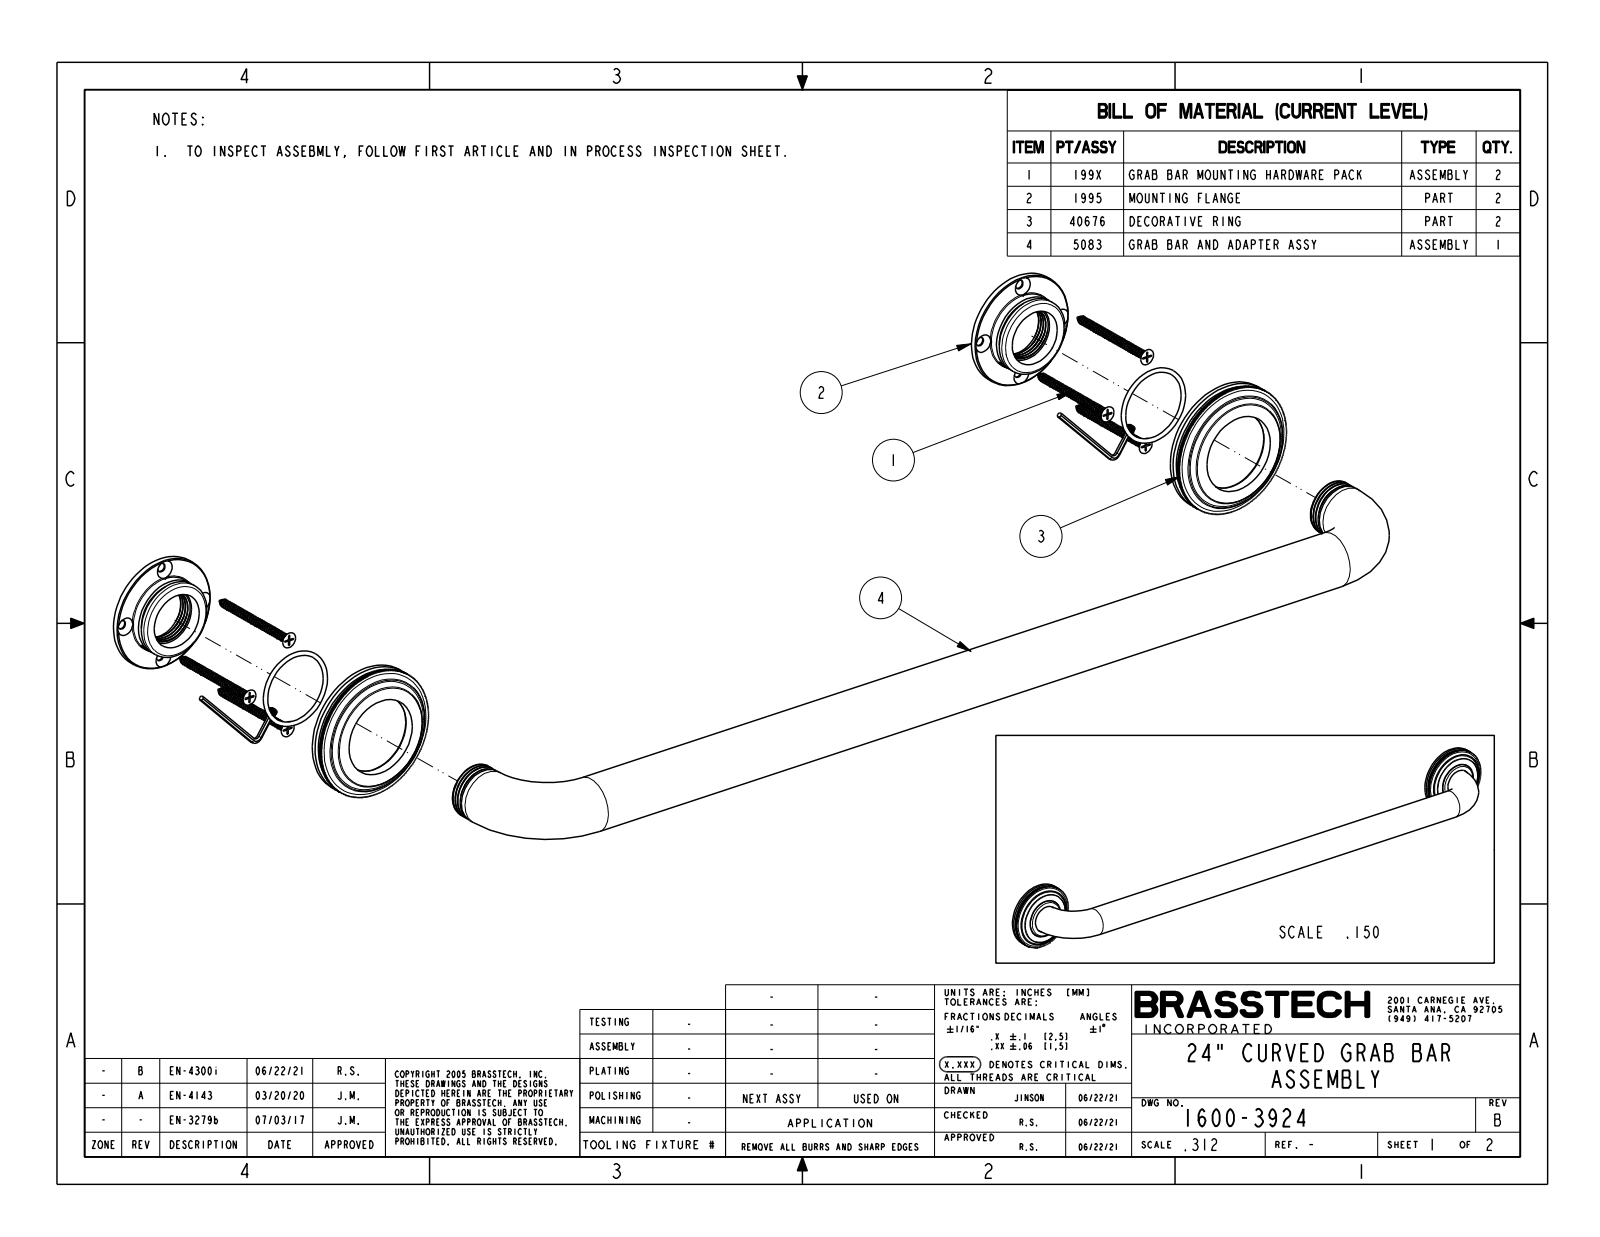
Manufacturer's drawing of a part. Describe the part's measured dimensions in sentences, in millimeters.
The part is named "1600-3924". Its 3-D file was written by "CREO PARAMETRIC BY PTC INC, 2018400 (CONFIG_CONTROL_DESIGN)". It is 1 solid with 1134 faces: 732 planar, 374 cylindrical and 28 other. Overall it measures 685.8 by 76.2 by 69.9 millimeters. Its volume is 628 400 cubic millimeters and its surface area 87 870 square millimeters. Round bosses or shafts: 2 of diameter 76.2, 2 of diameter 73.7, 2 of diameter 44.5, 1 of diameter 31.8. The main face-to-face distances are 13.3, 15.2, 1.9, 8.3, 5.1, 7, 2.5, 6.4, 1.9, 7.
